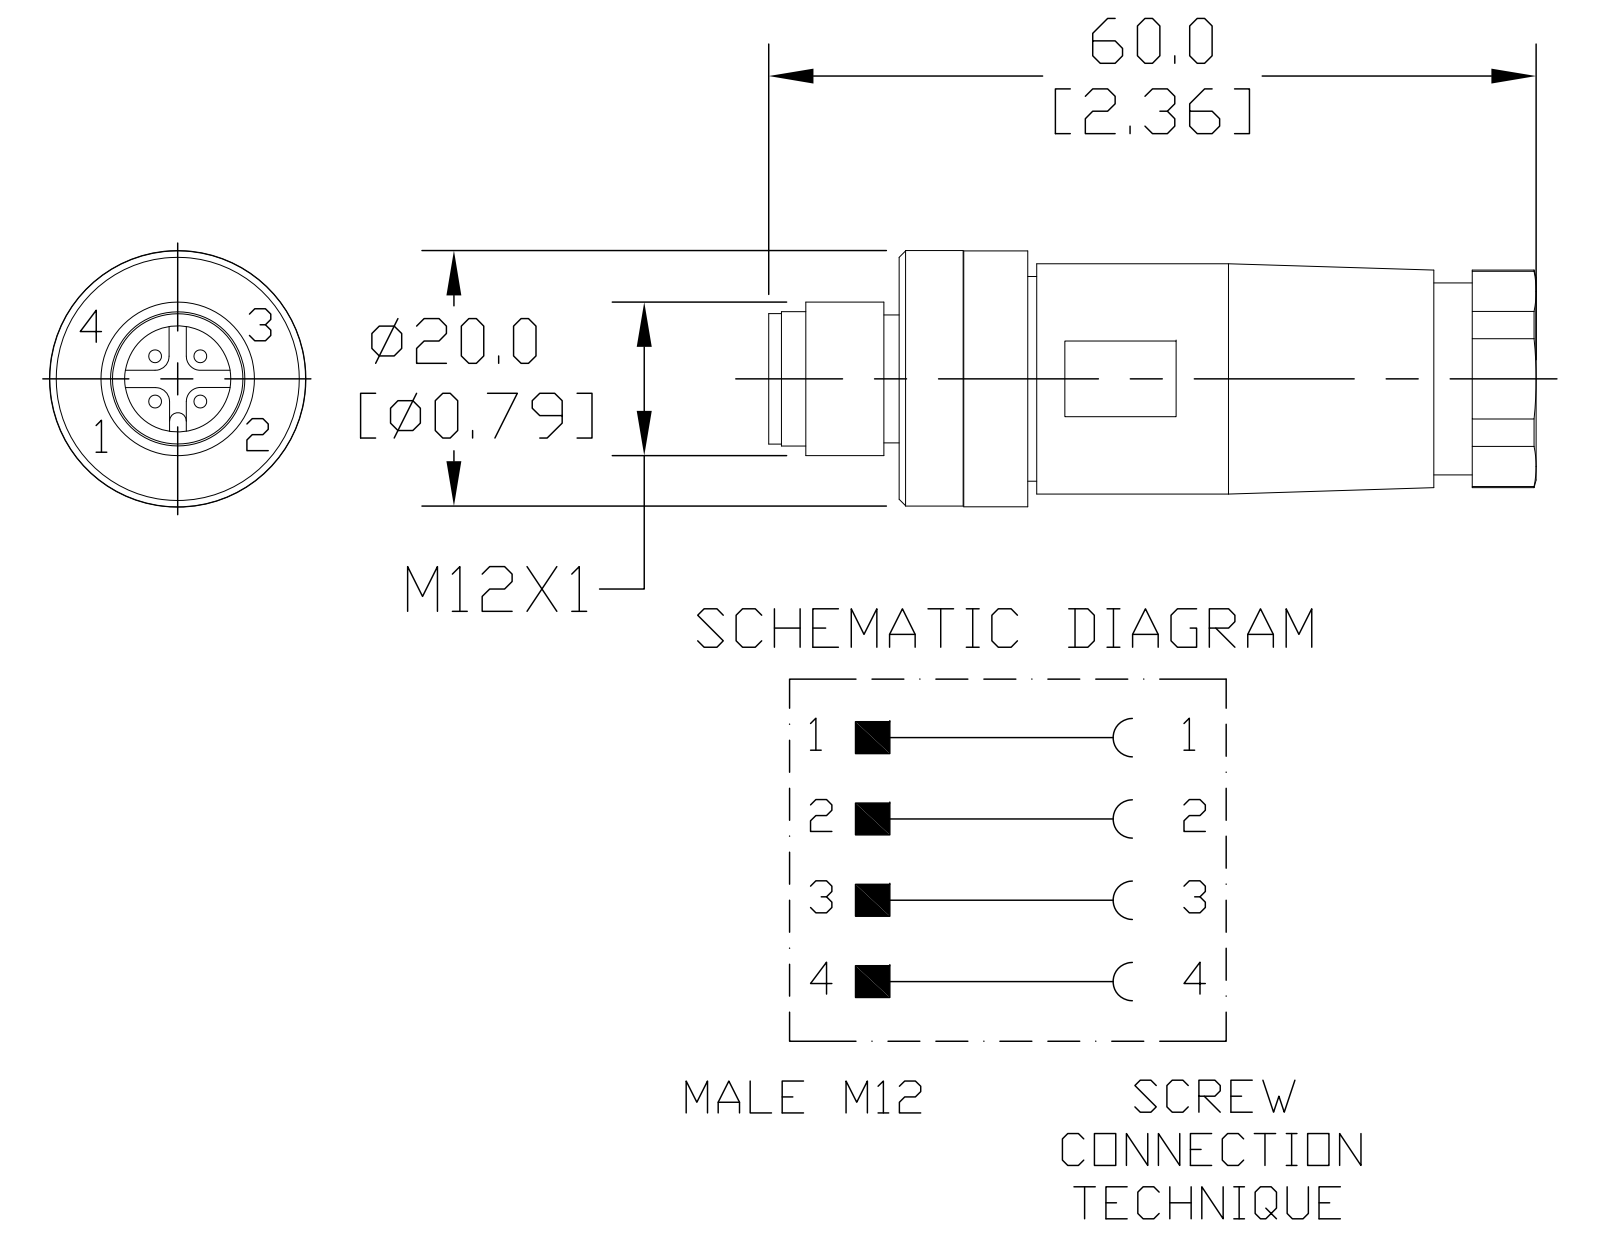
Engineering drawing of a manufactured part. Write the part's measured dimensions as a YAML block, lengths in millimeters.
part_name: "7000-12741-0000000"
step_written_by: "SolidWorks 2015 (AUTOMOTIVE_DESIGN)"
units: millimeters
bodies: {solids: 1, faces: 815, planar: 401, cylindrical: 223, other: 191}
overall_size: [60, 20, 19.99]
volume: 11343
surface_area: 5721
round_holes:
  - {diameter: 8.25, count: 1}
  - {diameter: 9.9, count: 1}
round_bosses_or_shafts:
  - {diameter: 1, count: 3}
  - {diameter: 17.78, count: 1}
  - {diameter: 11.07, count: 1}
  - {diameter: 10.66, count: 1}
  - {diameter: 9.09, count: 1}
  - {diameter: 8.95, count: 1}
  - {diameter: 1.03, count: 1}
partial_cylinders:
  - {radius: 0.62, count: 1}
  - {radius: 8.5, count: 1}
  - {radius: 10, count: 1}
face_to_face_distances: [4.91, 0.75, 15.75, 15, 44.93, 49.84, 6.02, 38.91, 43.82, 45]
